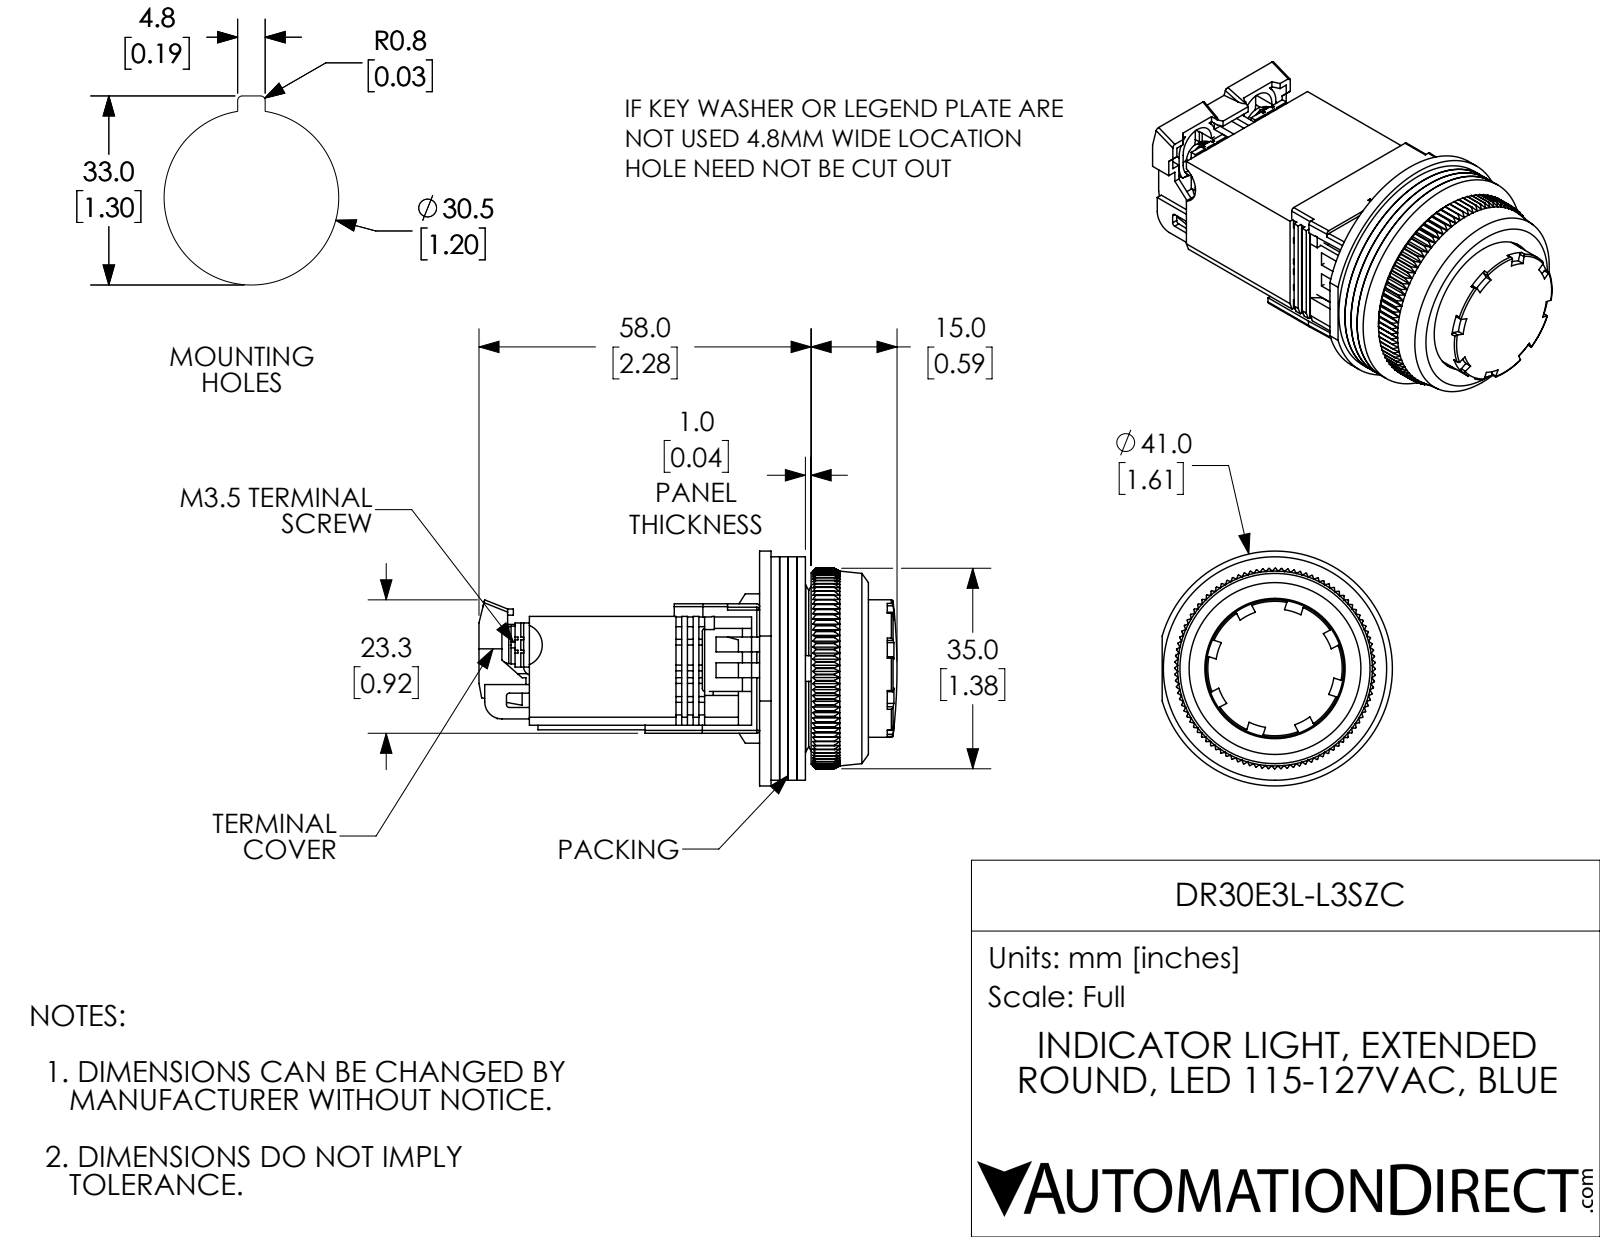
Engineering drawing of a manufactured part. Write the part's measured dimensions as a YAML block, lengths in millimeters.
part_name: "DR30E3L-L3SZC"
step_written_by: "SolidWorks 2017 (AUTOMOTIVE_DESIGN)"
units: millimeters
bodies: {solids: 19, faces: 1662, planar: 1058, cylindrical: 340, other: 264}
overall_size: [73, 41, 40.2]
volume: 37990
surface_area: 34230
round_holes:
  - {diameter: 3, count: 2}
  - {diameter: 3.5, count: 2}
  - {diameter: 3.6, count: 2}
  - {diameter: 11.8, count: 1}
  - {diameter: 14.3, count: 1}
  - {diameter: 18.3, count: 1}
  - {diameter: 20, count: 1}
  - {diameter: 22, count: 1}
  - {diameter: 24.5, count: 1}
  - {diameter: 28.5, count: 1}
  - {diameter: 29.8, count: 1}
  - {diameter: 30, count: 1}
round_bosses_or_shafts:
  - {diameter: 6.6, count: 2}
  - {diameter: 1.6, count: 2}
  - {diameter: 41, count: 1}
  - {diameter: 39, count: 1}
  - {diameter: 29.5, count: 1}
  - {diameter: 24, count: 1}
  - {diameter: 21.8, count: 1}
  - {diameter: 20.8, count: 1}
partial_cylinders:
  - {radius: 0.5, count: 24}
  - {radius: 0.3, count: 16}
  - {radius: 1.5, count: 9}
  - {radius: 3.5, count: 2}
  - {radius: 4.5, count: 2}
  - {radius: 0.4, count: 1}
  - {radius: 1.4, count: 1}
  - {radius: 3, count: 1}
face_to_face_distances: [1.5, 3, 1, 4.5, 5, 2, 6.5, 8, 19, 3.5]
hole_center_spacings: [8.5, 0.5, 8.2, 14.8, 14.8]
